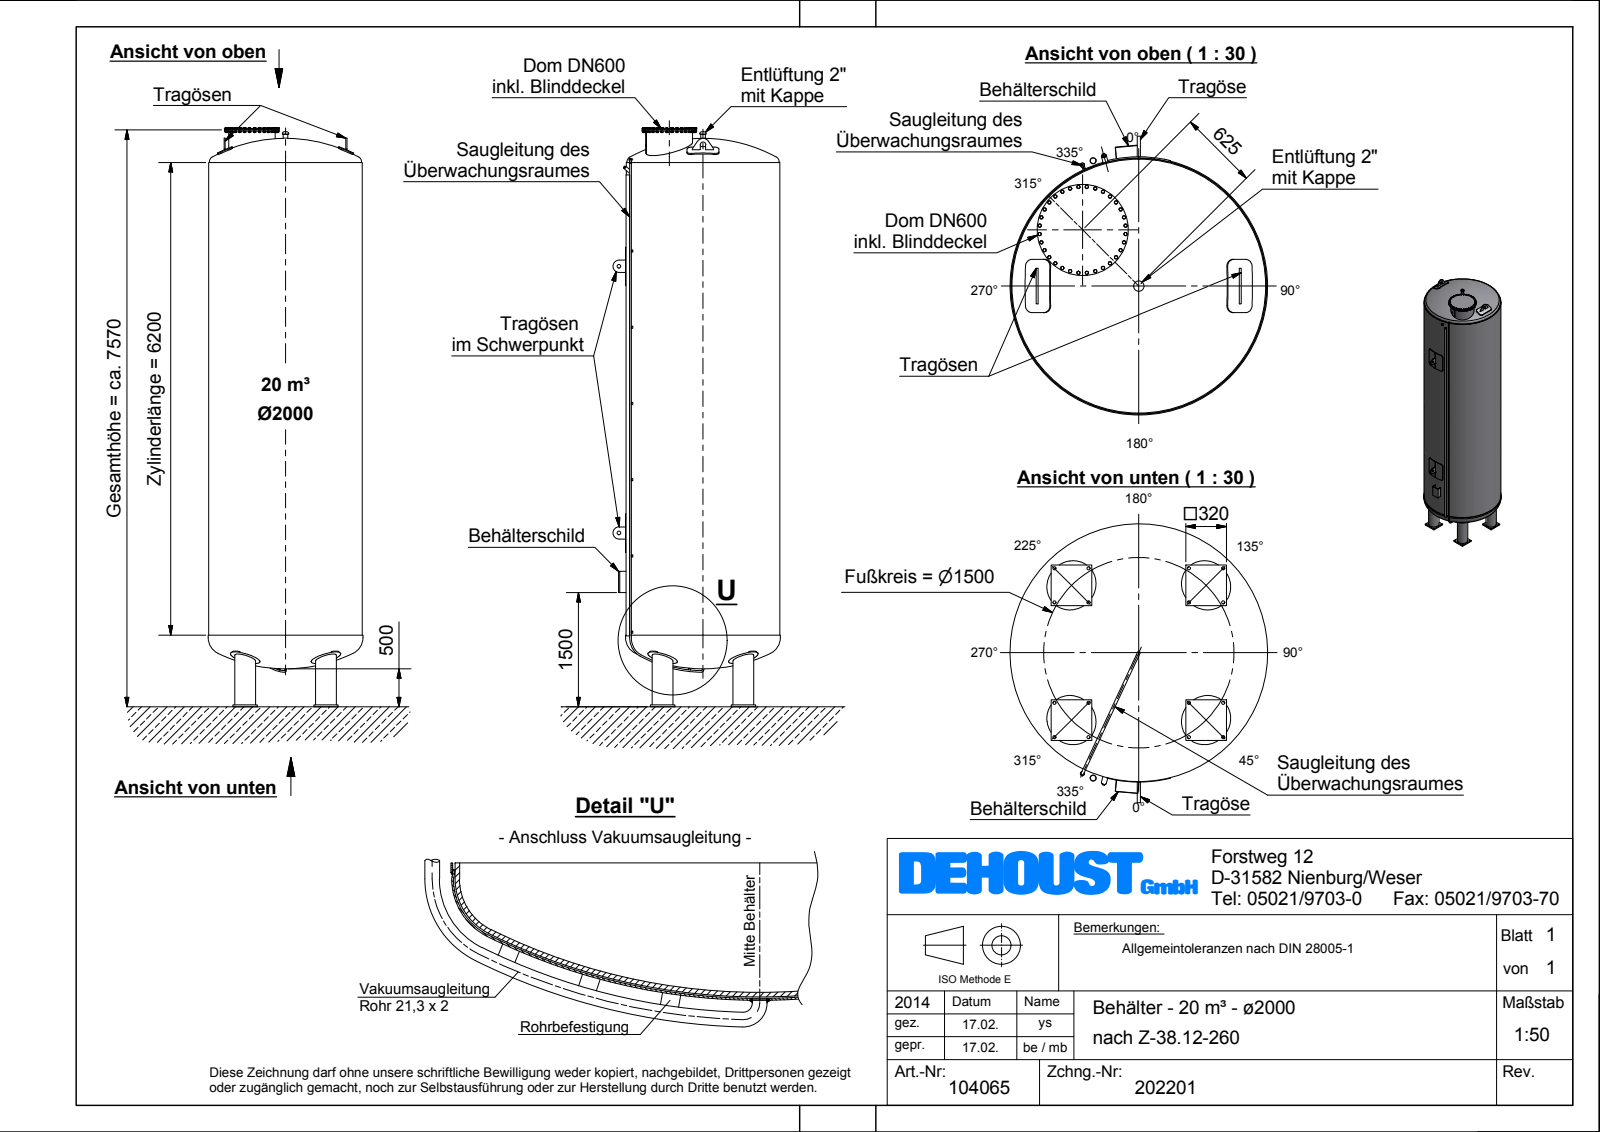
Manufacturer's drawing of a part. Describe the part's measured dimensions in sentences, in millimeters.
The part is named "Z-38_12-260_Beh\\S\\dlter_\\S\\x2000_020m\\S\\3_Dichte=1,0". Its 3-D file was written by "Autodesk Inventor 2012 (AUTOMOTIVE_DESIGN)". It is 10 solids with 1204 faces: 718 planar, 158 cylindrical and 328 other. Overall it measures 7599.18 by 2195 by 2030 millimeters. Its volume is 20 870 000 000 cubic millimeters and its surface area 62 800 000 square millimeters. Round holes: 4 of diameter 257, 1 of diameter 598, 1 of diameter 1988. Round bosses or shafts: 32 of diameter 22.5, 32 of diameter 16, 4 of diameter 400, 4 of diameter 273, 2 of diameter 21.3, 1 of diameter 2030, 1 of diameter 2016, 1 of diameter 2000. Partial cylindrical surfaces (rounded edges, fillets, slot ends): 8 of radius 50, 8 of radius 56, 2 of radius 80, 1 of radius 35, 1 of radius 85, 1 of radius 1018. The main face-to-face distances are 25, 7142.2, 7589.17, 446.97, 7554.17, 411.97, 35, 7117.2, 7529.17, 7564.17. The hole center spacings are 750, 1060.66, 976.28, 1500, 125, 625, 1375.
